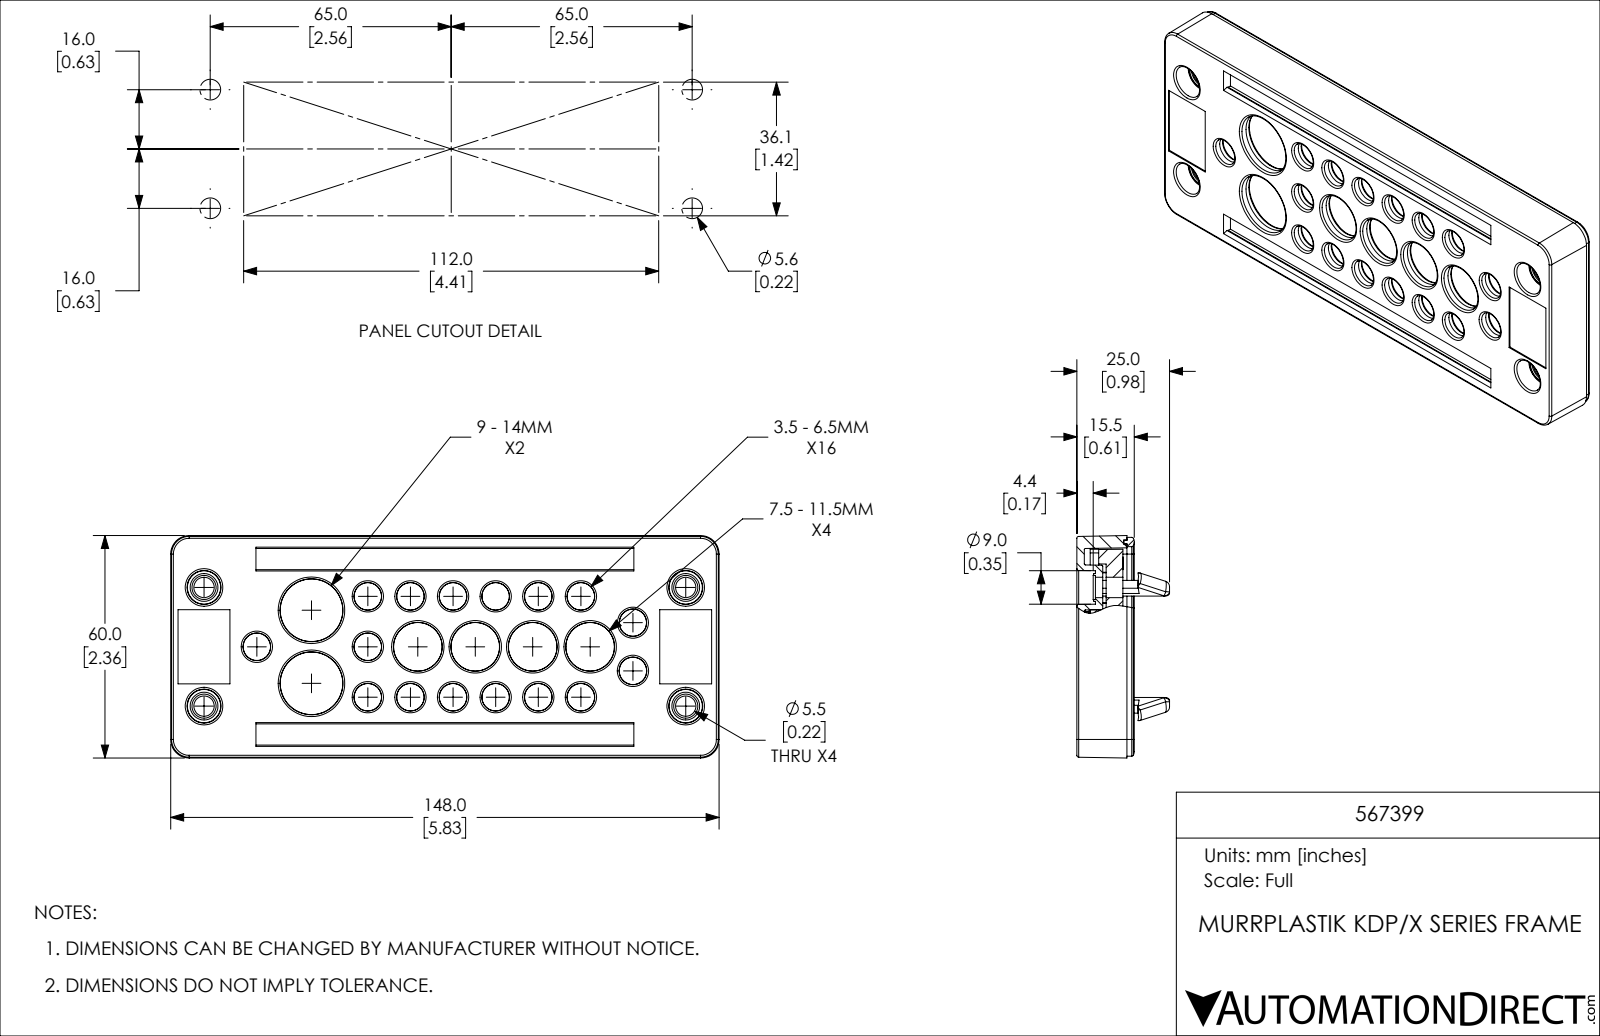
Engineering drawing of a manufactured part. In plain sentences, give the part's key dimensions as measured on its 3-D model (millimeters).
The part is named "567399". Its 3-D file was written by "SolidWorks 2019 (CONFIG_CONTROL_DESIGN)". It is 4 solids with 3002 faces: 902 planar, 994 cylindrical and 1106 other. Overall it measures 148 by 60 by 25 millimeters. Its volume is 72 324 cubic millimeters and its surface area 70 906 square millimeters. Round holes: 16 of diameter 10.5, 10 of diameter 3.6, 10 of diameter 3.8, 4 of diameter 5.5, 4 of diameter 6.5, 4 of diameter 14.5, 3 of diameter 2.6, 2 of diameter 5, 2 of diameter 18, 1 of diameter 3, 1 of diameter 3.1. Round bosses or shafts: 4 of diameter 7.5, 3 of diameter 2.5. Partial cylindrical surfaces (rounded edges, fillets, slot ends): 108 of radius 0.3, 82 of radius 0.5, 32 of radius 0.45, 16 of radius 1, 16 of radius 1.5, 15 of radius 6.85, 12 of radius 2, 8 of radius 3.5. The main face-to-face distances are 2.3, 3.3, 5.9, 3.6, 6.5, 2, 8.8, 12.4, 3.8, 3.9. The hole center spacings are 11.5, 23, 26.59, 35.31, 42.8, 62.1, 65.75, 69.74.
